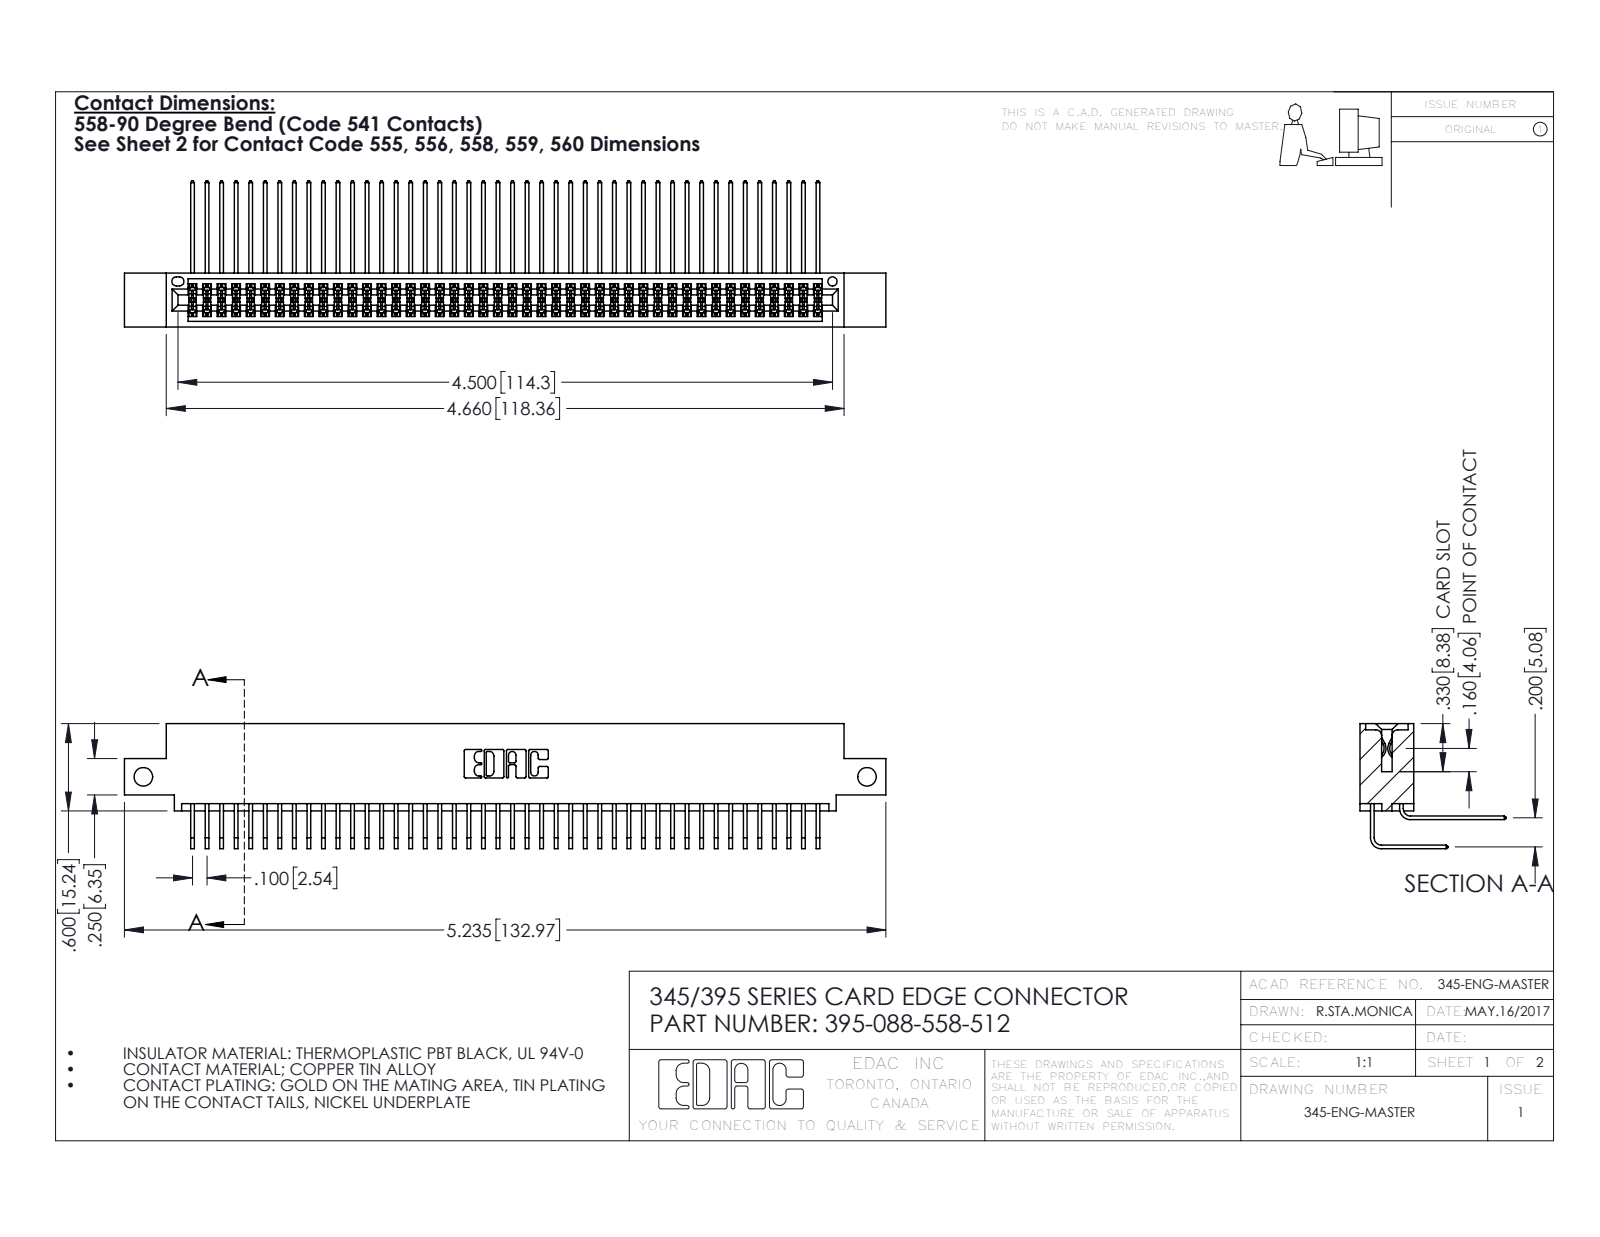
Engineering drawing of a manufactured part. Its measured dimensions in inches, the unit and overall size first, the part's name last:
Units: inches
Overall size (bounding box): 5.235 × 1.005 × 0.859
Round holes (diameter × count): ⌀0.128 ×2, ⌀0.064 ×1
Partial cylindrical surfaces — rounded edges, fillets, slot ends (radius × count): R0.006 ×133, R0.01 ×22, R0.007 ×6, R0.031 ×6, R0.026 ×3, R0.014 ×2, R0.019 ×2, R0.022 ×2
Main face-to-face distances: 0.072, 0.298, 0.2, 0.37, 0.098, 0.272, 0.025, 0.225, 0.025, 0.175
Hole centre spacings: 4.975
Volume: 0.811 in³ · Surface area: 34.13 in²
Bodies: 89 solids, 4706 faces (3164 planar, 1542 cylindrical, 0 other)
Part name (STEP PRODUCT): 345-292-001_558 559 Tail - 1; 345-292-001_558 Tail - 2; 395-088-558-512; 345 Part_0.110 Offset - Side Mount
STEP written by: SolidWorks 2016 (CONFIG_CONTROL_DESIGN)
